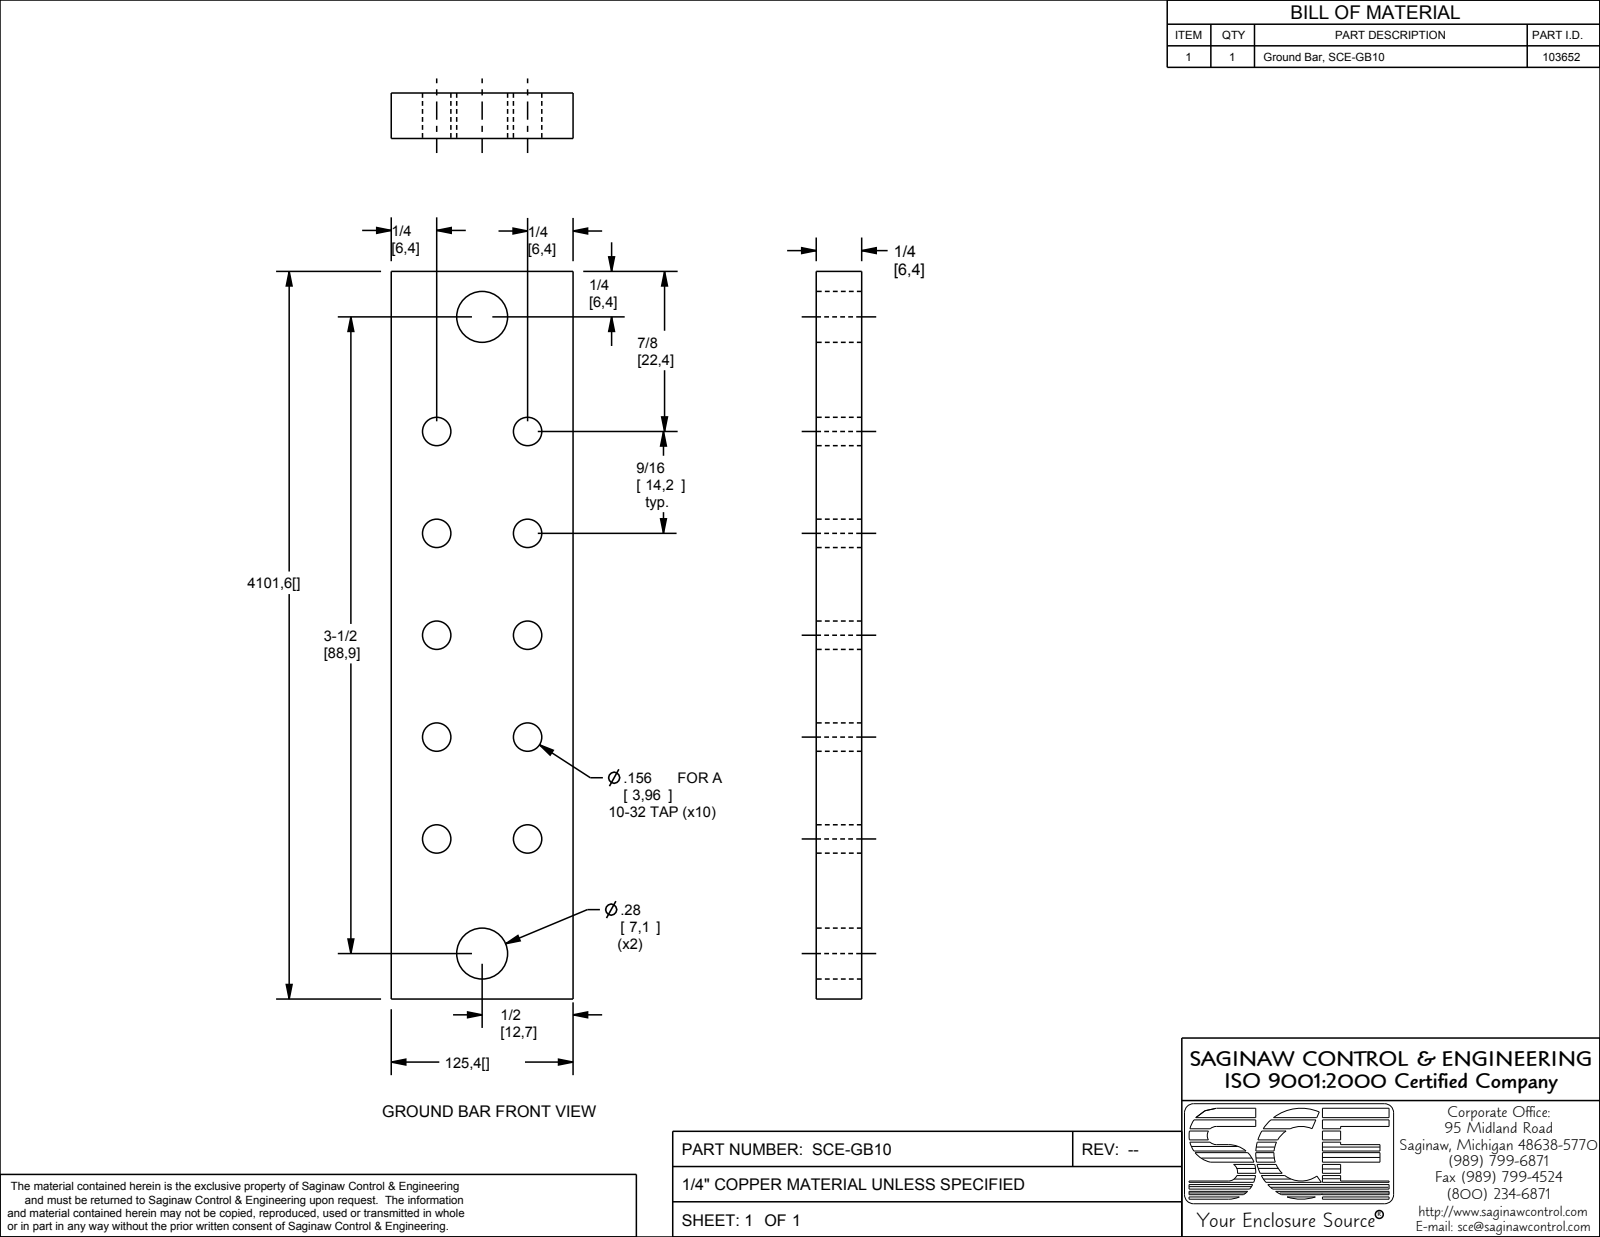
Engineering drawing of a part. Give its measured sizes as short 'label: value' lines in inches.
name: SCE-GB10
written by: SolidWorks 2019 (AUTOMOTIVE_DESIGN)
unit: in
bodies: 1 solid, 18 faces (6 planar, 12 cylindrical, 0 other)
size: 4 × 1 × 0.25
volume: 0.921 in³; area: 11.54 in²
holes: 10× ⌀0.156, 2× ⌀0.28
face distances: 0.25, 1, 4
hole spacings: 0.751, 0.5, 0.56, 0.56, 0.678, 1.12, 1.216, 1.227
